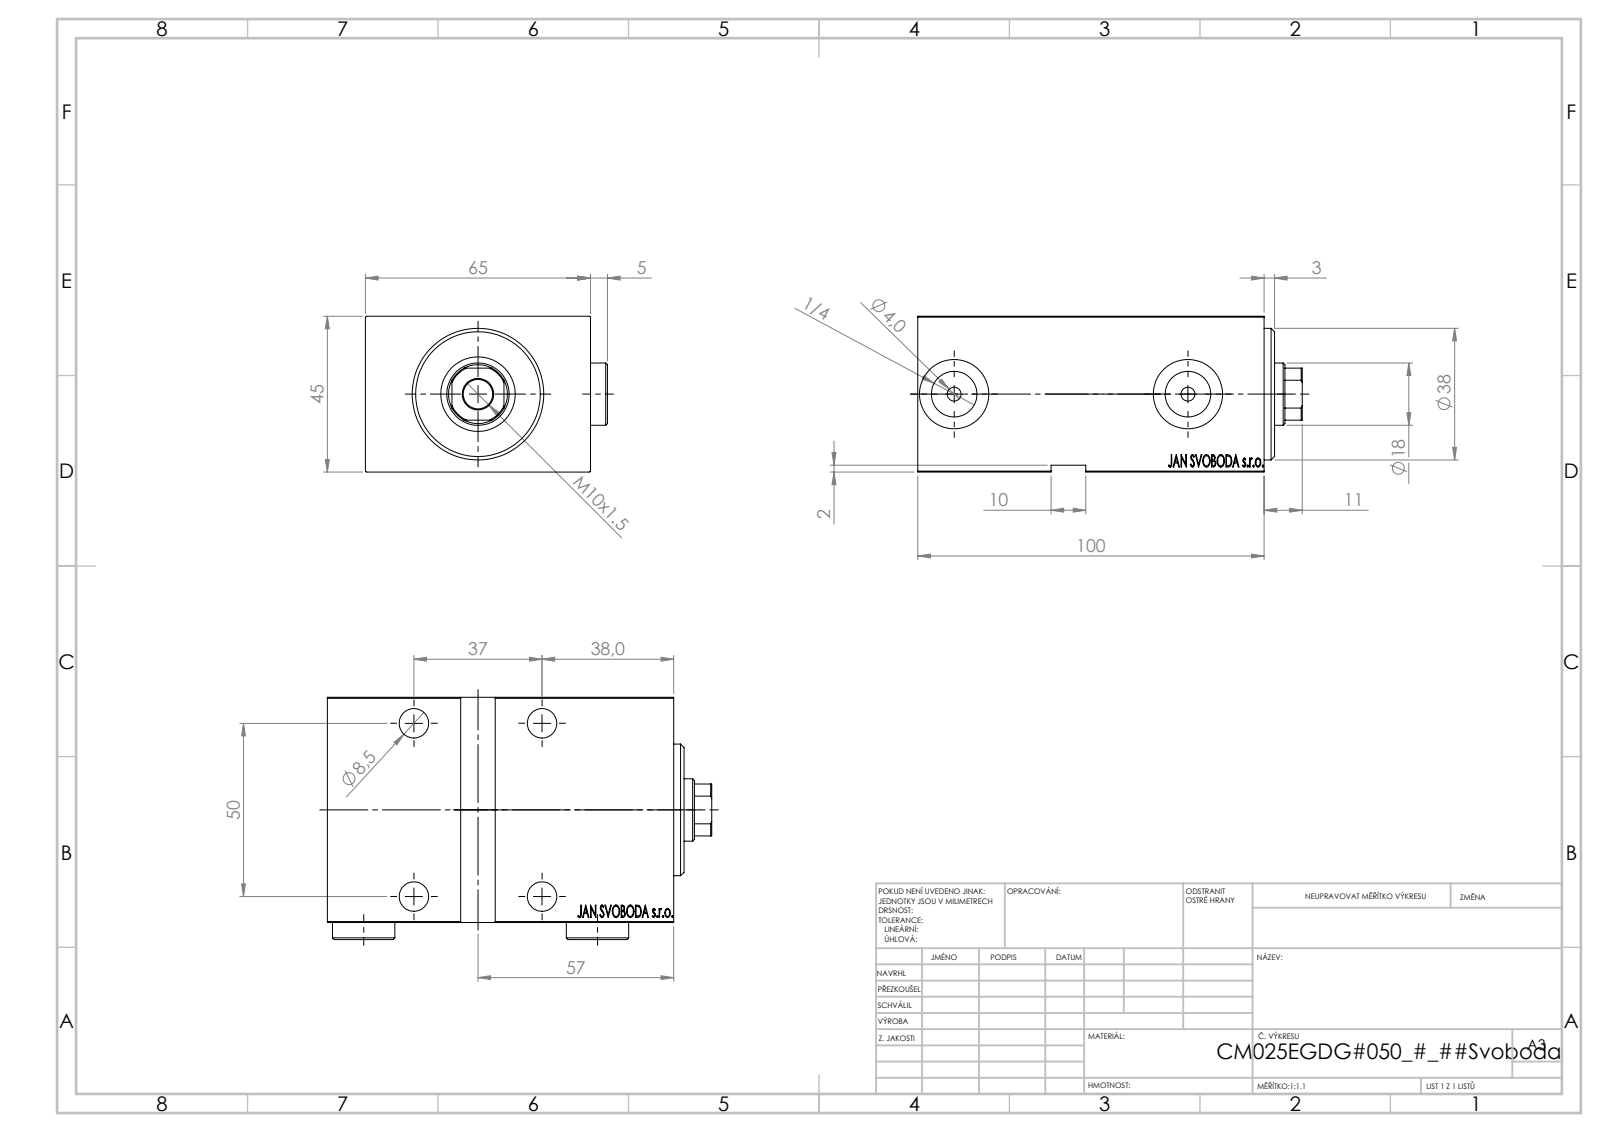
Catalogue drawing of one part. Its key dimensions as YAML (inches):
part_name: "Zatka_OIL_PORT; V450CM_VC_B; V450CM_E_Body; V450CM_E_VCP"
step_written_by: "SolidWorks 2019 (CONFIG_CONTROL_DESIGN)"
units: inches
bodies: {solids: 5, faces: 910, planar: 444, cylindrical: 68, other: 398}
overall_size: [4.37, 2.752, 1.772]
volume: 16.23
surface_area: 89.18
round_holes:
  - {diameter: 0.335, count: 5}
  - {diameter: 0.531, count: 4}
  - {diameter: 0.157, count: 2}
  - {diameter: 0.518, count: 2}
  - {diameter: 0.787, count: 2}
  - {diameter: 0.709, count: 1}
  - {diameter: 0.846, count: 1}
  - {diameter: 0.984, count: 1}
  - {diameter: 1.378, count: 1}
round_bosses_or_shafts:
  - {diameter: 0.709, count: 2}
  - {diameter: 1.496, count: 1}
  - {diameter: 1.063, count: 1}
partial_cylinders:
  - {radius: 0.335, count: 1}
face_to_face_distances: [1.772, 2.559, 3.937, 0.197, 2.555, 0.236, 3.701, 3.74, 3.504, 0.315]
hole_center_spacings: [1.457, 1.969, 2.449, 2.657]
